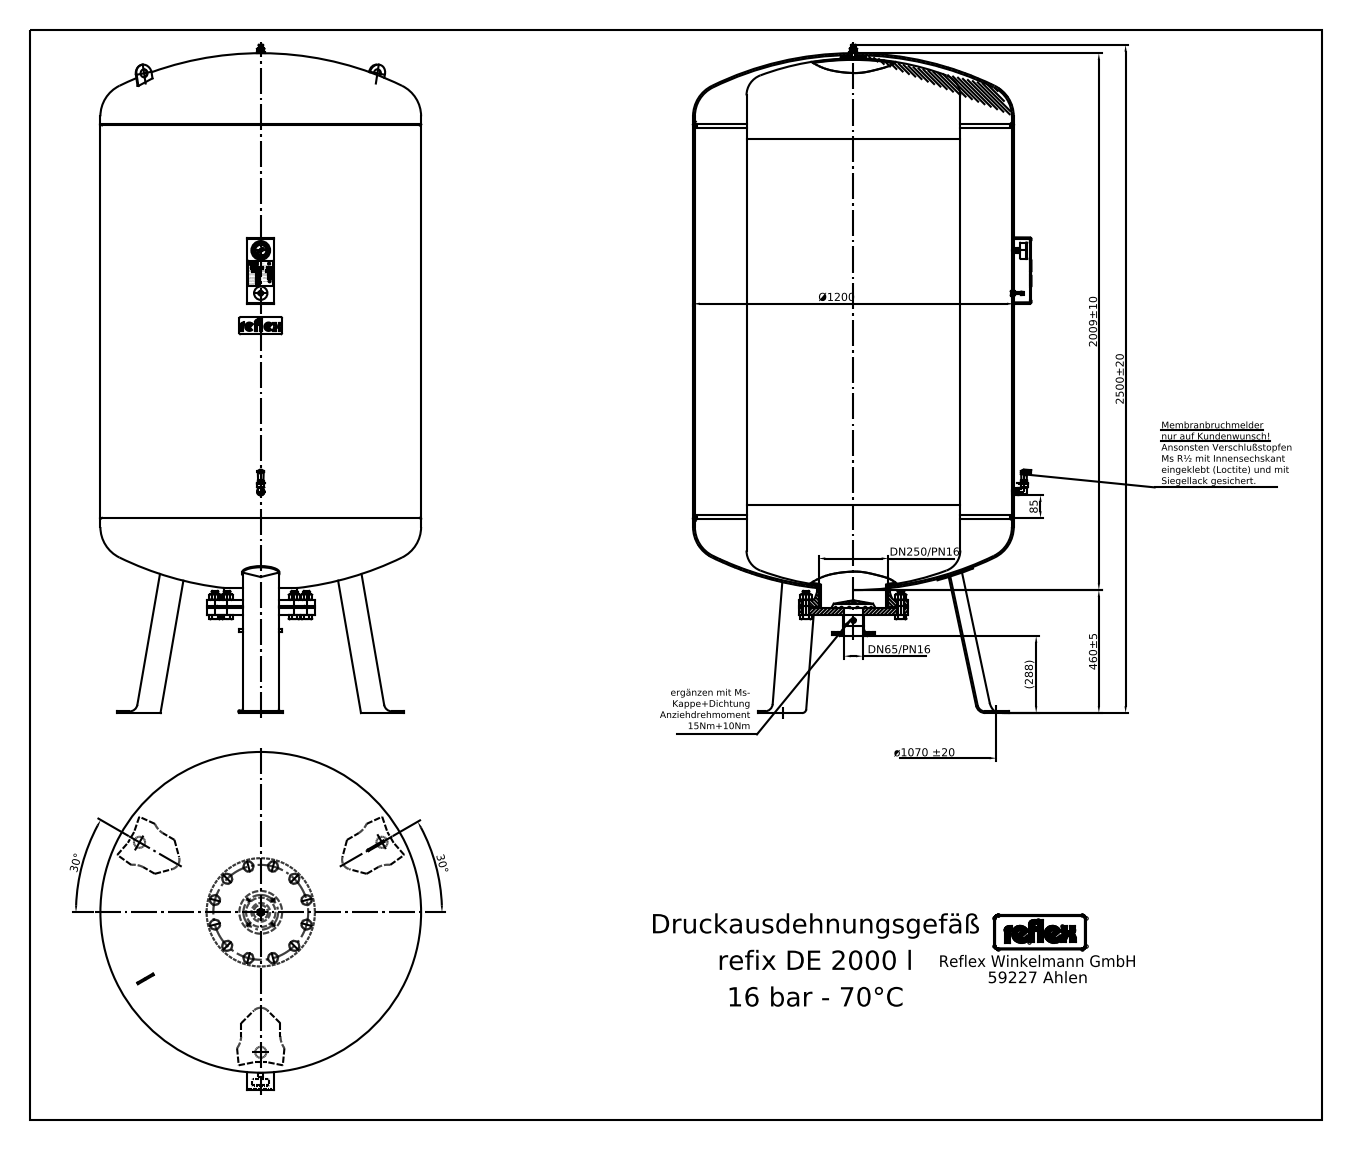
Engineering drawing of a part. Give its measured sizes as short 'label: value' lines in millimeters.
written by: Mechanical Desktop 2008 (CONFIG_CONTROL_DESIGN)
unit: mm
bodies: 23 solids, 612 faces (340 planar, 155 cylindrical, 117 other)
size: 2500 × 1266 × 1200
volume: 2 098 000 000 mm³; area: 14 900 000 mm²
holes: 1× ⌀10, 1× ⌀30, 1× ⌀50, 1× ⌀69, 1× ⌀260.4
bosses: 13× ⌀16, 2× ⌀28, 2× ⌀26, 2× ⌀20, 1× ⌀1200, 1× ⌀405, 1× ⌀273, 1× ⌀76.1
rounds: 18× R25, 4× R5.62, 3× R2.25, 3× R9, 2× R1, 2× R3.84, 2× R5, 2× R6.75
face distances: 1499, 26, 313, 1812, 339, 1838, 31, 5.97, 5.89, 57
hole spacings: 82.33, 615.5, 737.57, 800.05
